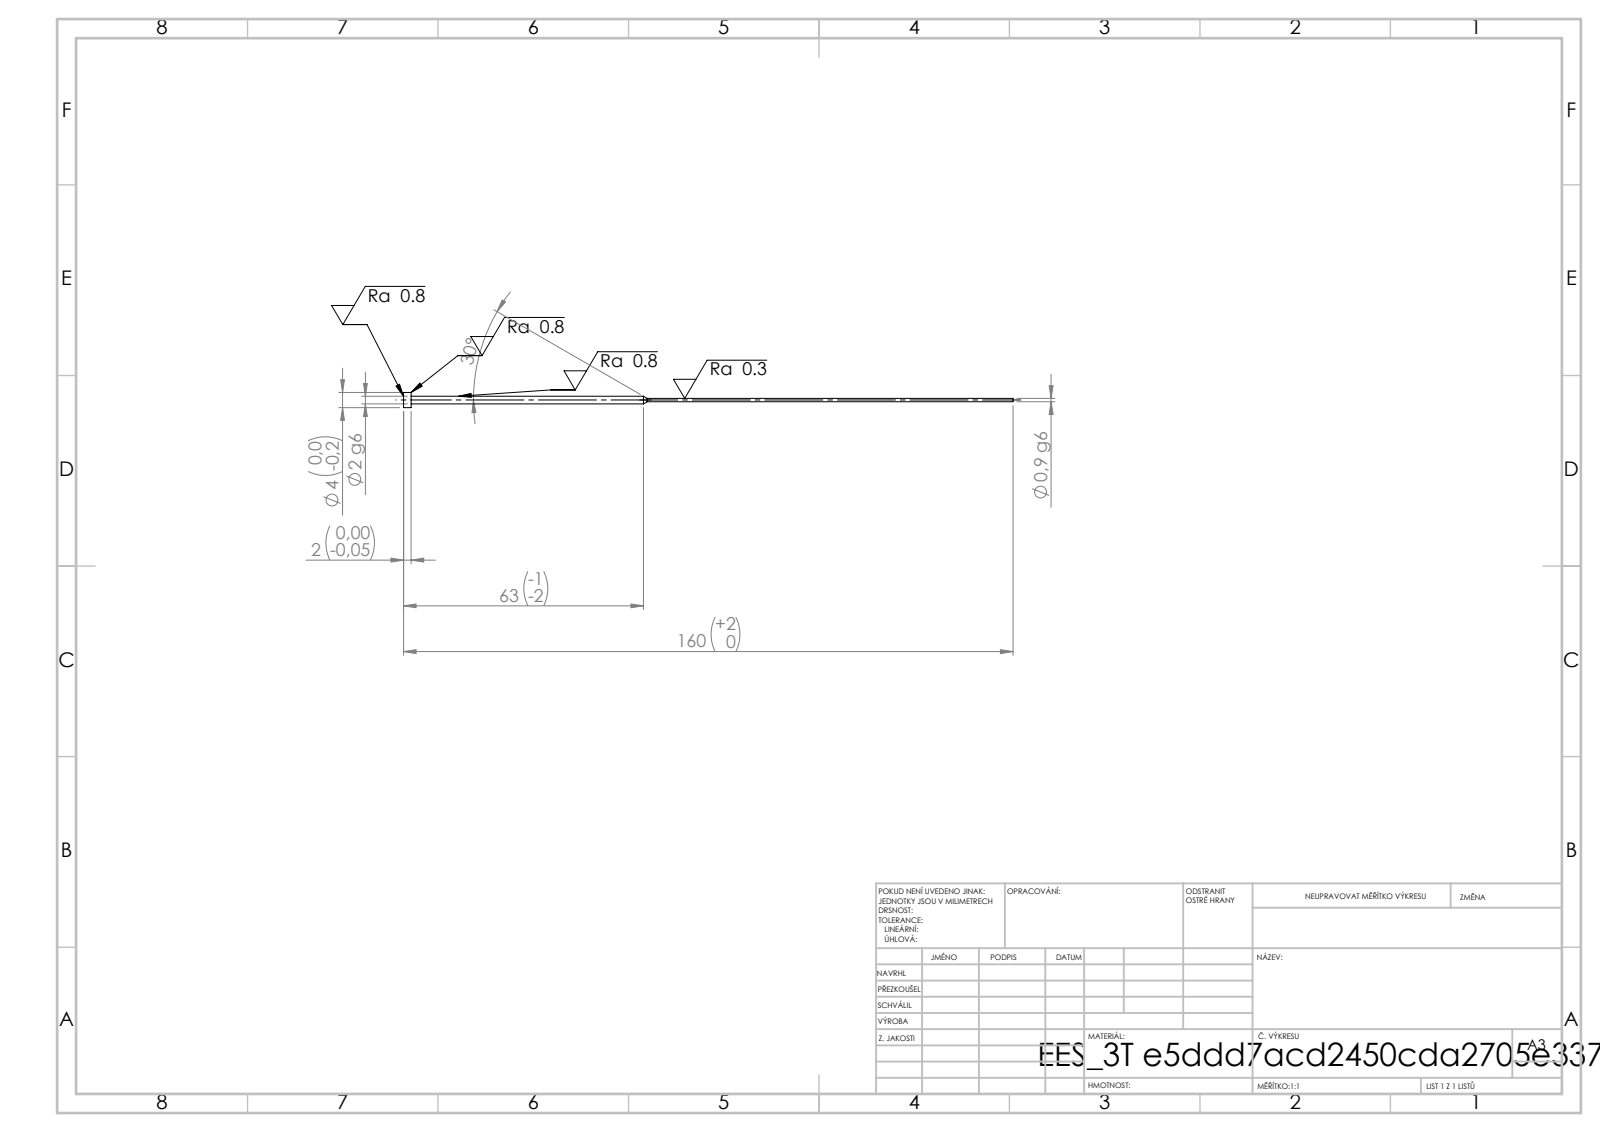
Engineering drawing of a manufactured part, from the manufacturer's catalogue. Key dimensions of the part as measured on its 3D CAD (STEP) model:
STEP written by: SolidWorks 2019 (CONFIG_CONTROL_DESIGN)
Units: millimetres
Bodies: 1 solid, 11 faces (3 planar, 6 cylindrical, 2 other)
Overall size (bounding box): 160 × 4 × 4
Volume: 280 mm³ · Surface area: 708 mm²
Round bosses / shafts (diameter × count): ⌀4 ×1, ⌀2 ×1, ⌀0.9 ×1
Main face-to-face distances: 2, 158, 160
